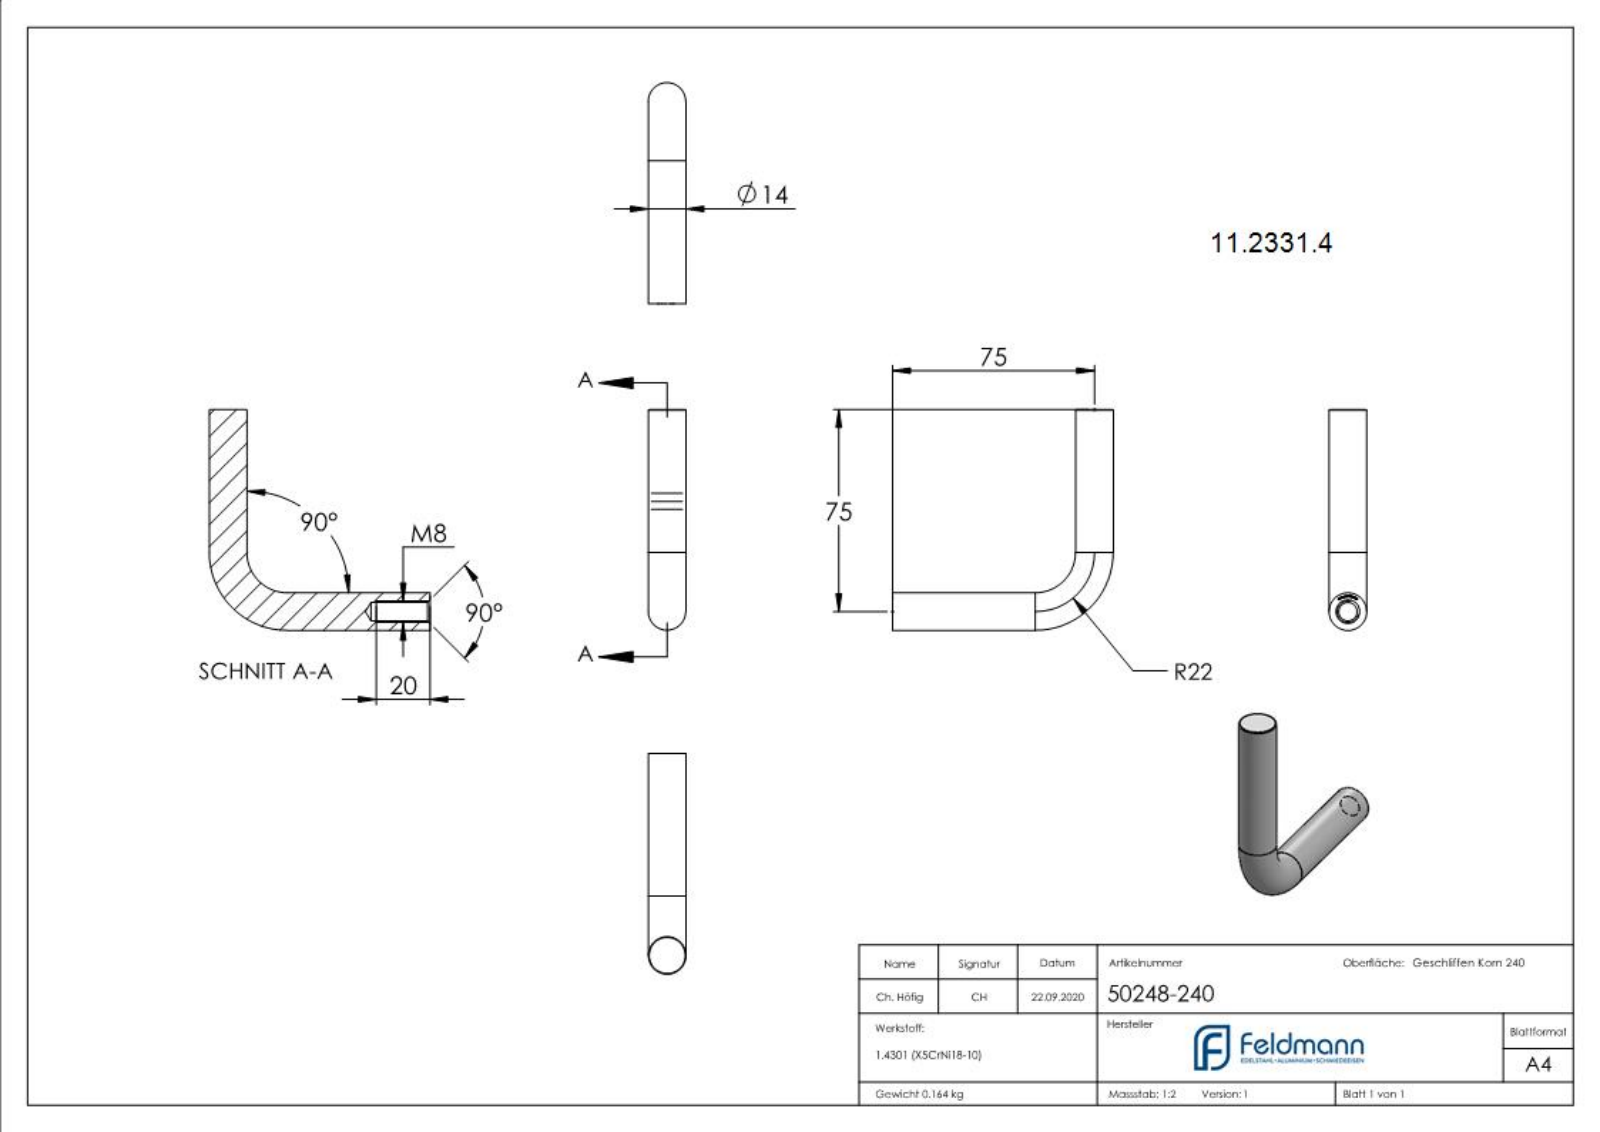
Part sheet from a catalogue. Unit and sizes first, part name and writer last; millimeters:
Units: millimetres
Overall size (bounding box): 82 × 82 × 14
Round holes (diameter × count): ⌀6.8 ×1
Round bosses / shafts (diameter × count): ⌀14 ×2
Main face-to-face distances: 0.34, 0.39, 0.53, 0.48, 0.4, 0.35, 0.31, 0.54, 0.55
Volume: 20 800 mm³ · Surface area: 6 951 mm²
Bodies: 1 solid, 247 faces (130 planar, 6 cylindrical, 111 other)
Part name (STEP PRODUCT): 50248-240
STEP written by: SolidWorks 2018 (CONFIG_CONTROL_DESIGN)
